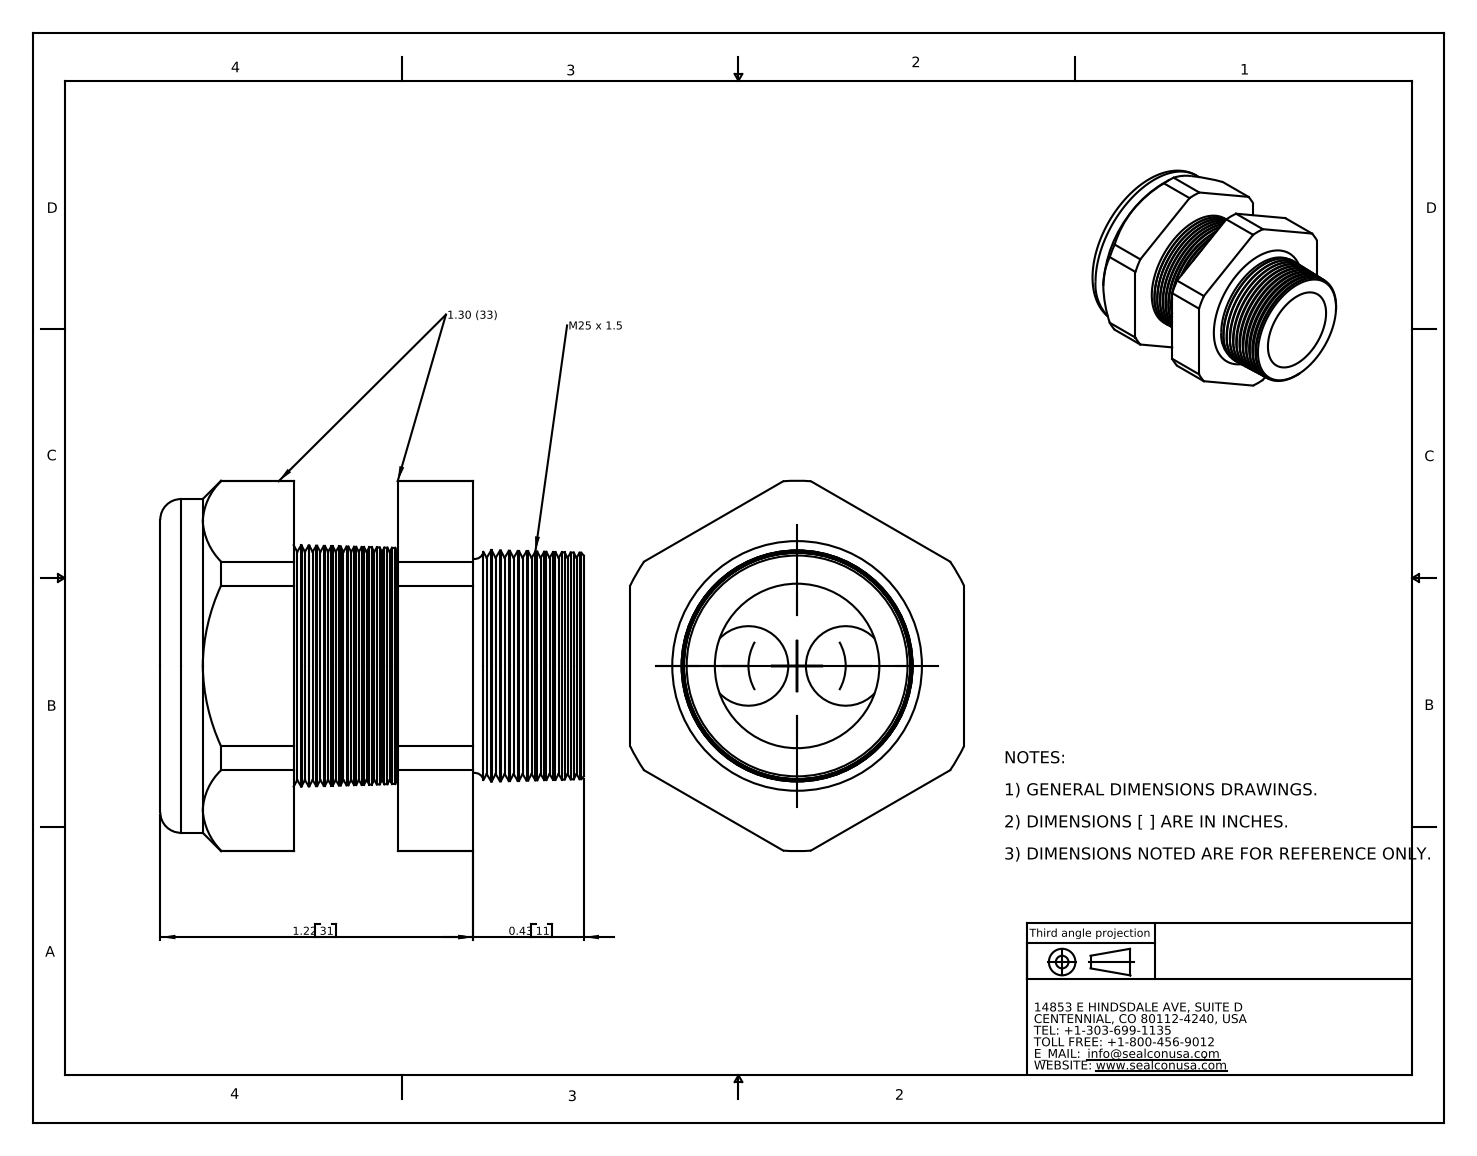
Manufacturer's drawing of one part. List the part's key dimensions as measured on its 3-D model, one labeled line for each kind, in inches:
Part name (STEP PRODUCT): CD25M3-GY
STEP written by: SolidWorks 2007 (CONFIG_CONTROL_DESIGN)
Units: inches
Bodies: 2 solids, 210 faces (20 planar, 24 cylindrical, 166 other)
Overall size (bounding box): 1.65 × 1.443 × 1.3
Volume: 1.141 in³ · Surface area: 16.9 in²
Round holes (diameter × count): ⌀0.31 ×2, ⌀0.69 ×1, ⌀0.71 ×1
Round bosses / shafts (diameter × count): ⌀1.3 ×1
Partial cylindrical surfaces — rounded edges, fillets, slot ends (radius × count): R0.721 ×1
Main face-to-face distances: 1.3, 0.405, 0.7, 0.295, 0.52, 0.925, 1.22, 1.65, 1.13, 0.725
Hole centre spacings: 0.189, 0.379
